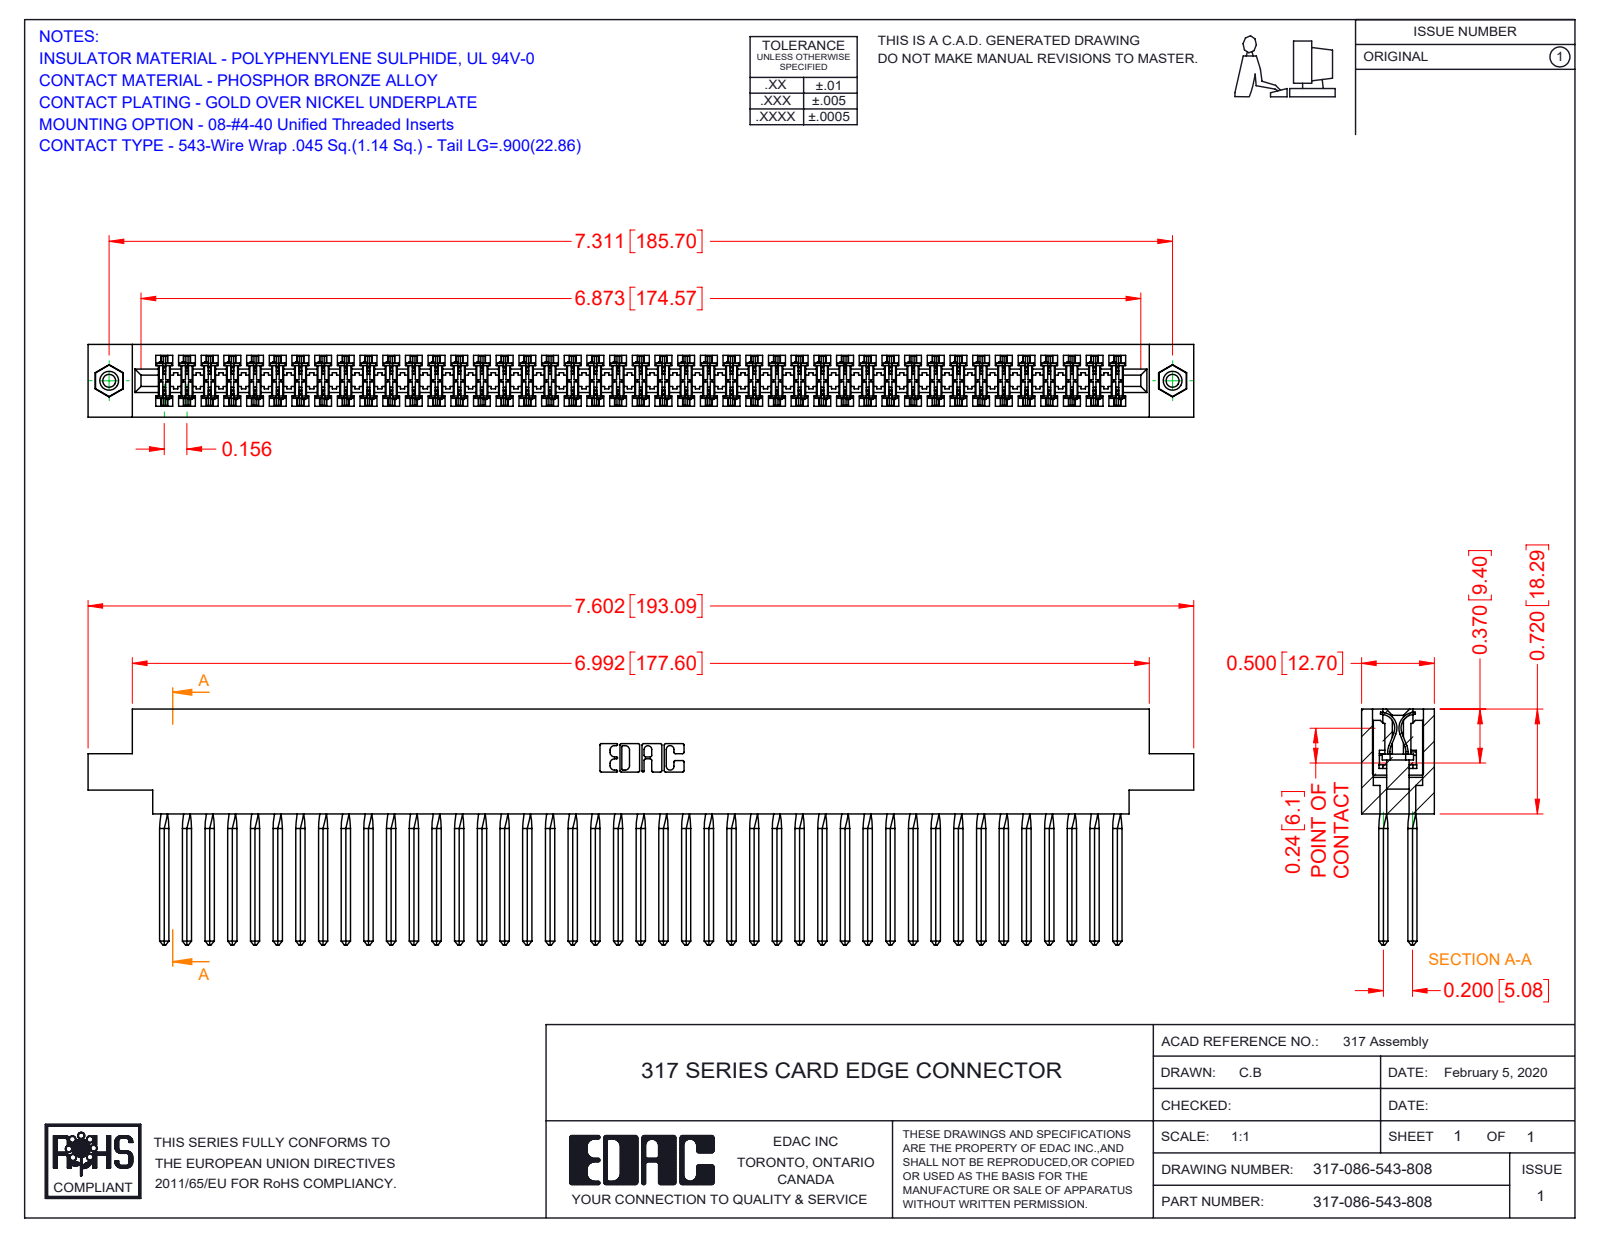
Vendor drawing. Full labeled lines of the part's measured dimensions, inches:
Part name (STEP PRODUCT): 317-290-001_543; 317-086-543-878; 317 Part_.156 Dia - TI; 345-250-001_345-250-003-102
STEP written by: SolidWorks 2016 (CONFIG_CONTROL_DESIGN)
Units: inches
Bodies: 89 solids, 7816 faces (6368 planar, 1088 cylindrical, 360 other)
Overall size (bounding box): 7.602 × 1.62 × 0.5
Volume: 2.005 in³ · Surface area: 77.37 in²
Round holes (diameter × count): ⌀0.089 ×2, ⌀0.125 ×2, ⌀0.156 ×2
Round bosses / shafts (diameter × count): ⌀0.155 ×2
Partial cylindrical surfaces — rounded edges, fillets, slot ends (radius × count): R0.015 ×172, R0.01 ×22, R0.007 ×6, R0.031 ×6, R0.026 ×3, R0.095 ×2, R0.1 ×2, R0.11 ×2
Main face-to-face distances: 0.5, 0.075, 0.425, 0.35, 0.195, 0.11, 0.094, 0.2, 0.115, 0.131
Hole centre spacings: 7.311
